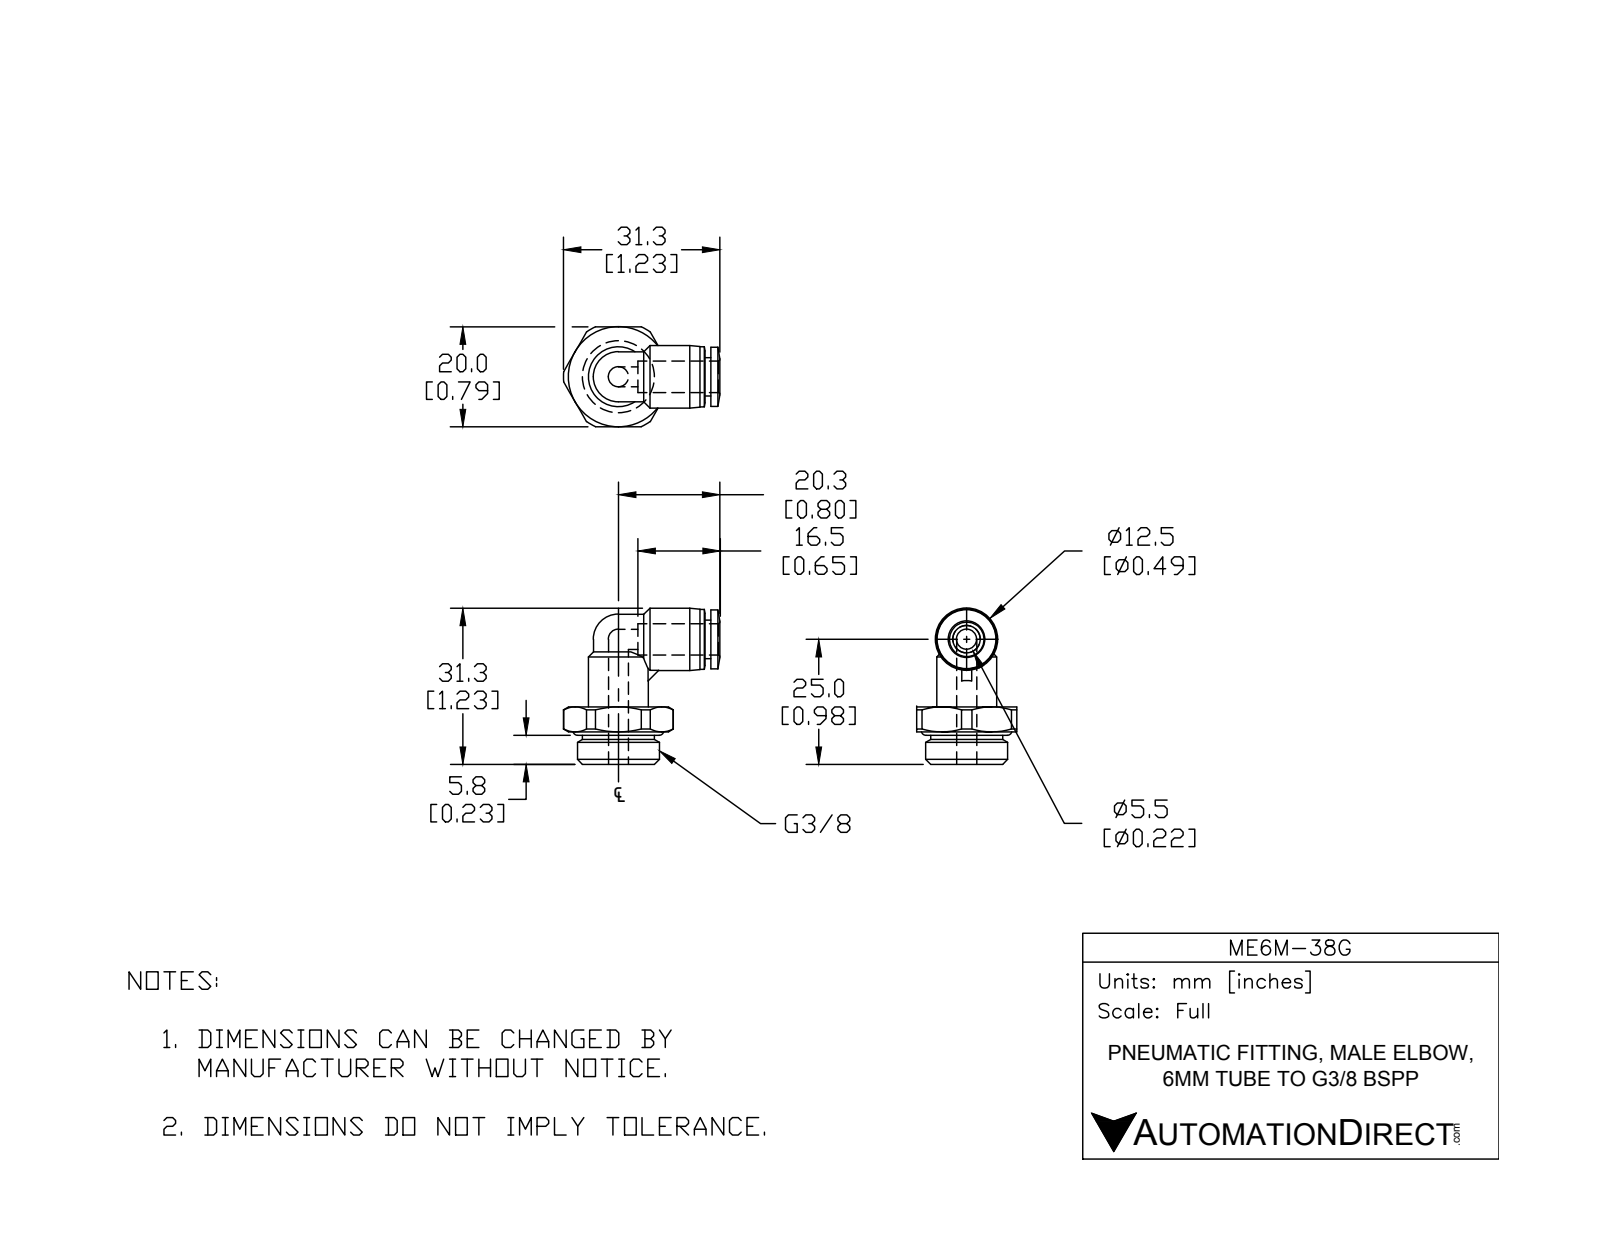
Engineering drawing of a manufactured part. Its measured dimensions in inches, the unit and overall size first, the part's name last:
Units: inches
Overall size (bounding box): 1.232 × 1.23 × 0.787
Round holes (diameter × count): ⌀0.157 ×2, ⌀0.248 ×1
Round bosses / shafts (diameter × count): ⌀0.472 ×2, ⌀0.646 ×1, ⌀0.567 ×1, ⌀0.492 ×1, ⌀0.465 ×1, ⌀0.303 ×1
Partial cylindrical surfaces — rounded edges, fillets, slot ends (radius × count): R0.197 ×2, R0.433 ×1
Main face-to-face distances: 0.453, 0.787, 0.045, 0.256, 0.197, 0.303, 0.047, 0.15, 0.53, 0.575
Volume: 0.343 in³ · Surface area: 5.761 in²
Bodies: 2 solids, 84 faces (18 planar, 29 cylindrical, 37 other)
Part name (STEP PRODUCT): ME6M-38G
STEP written by: SolidWorks 2018 (AUTOMOTIVE_DESIGN)
